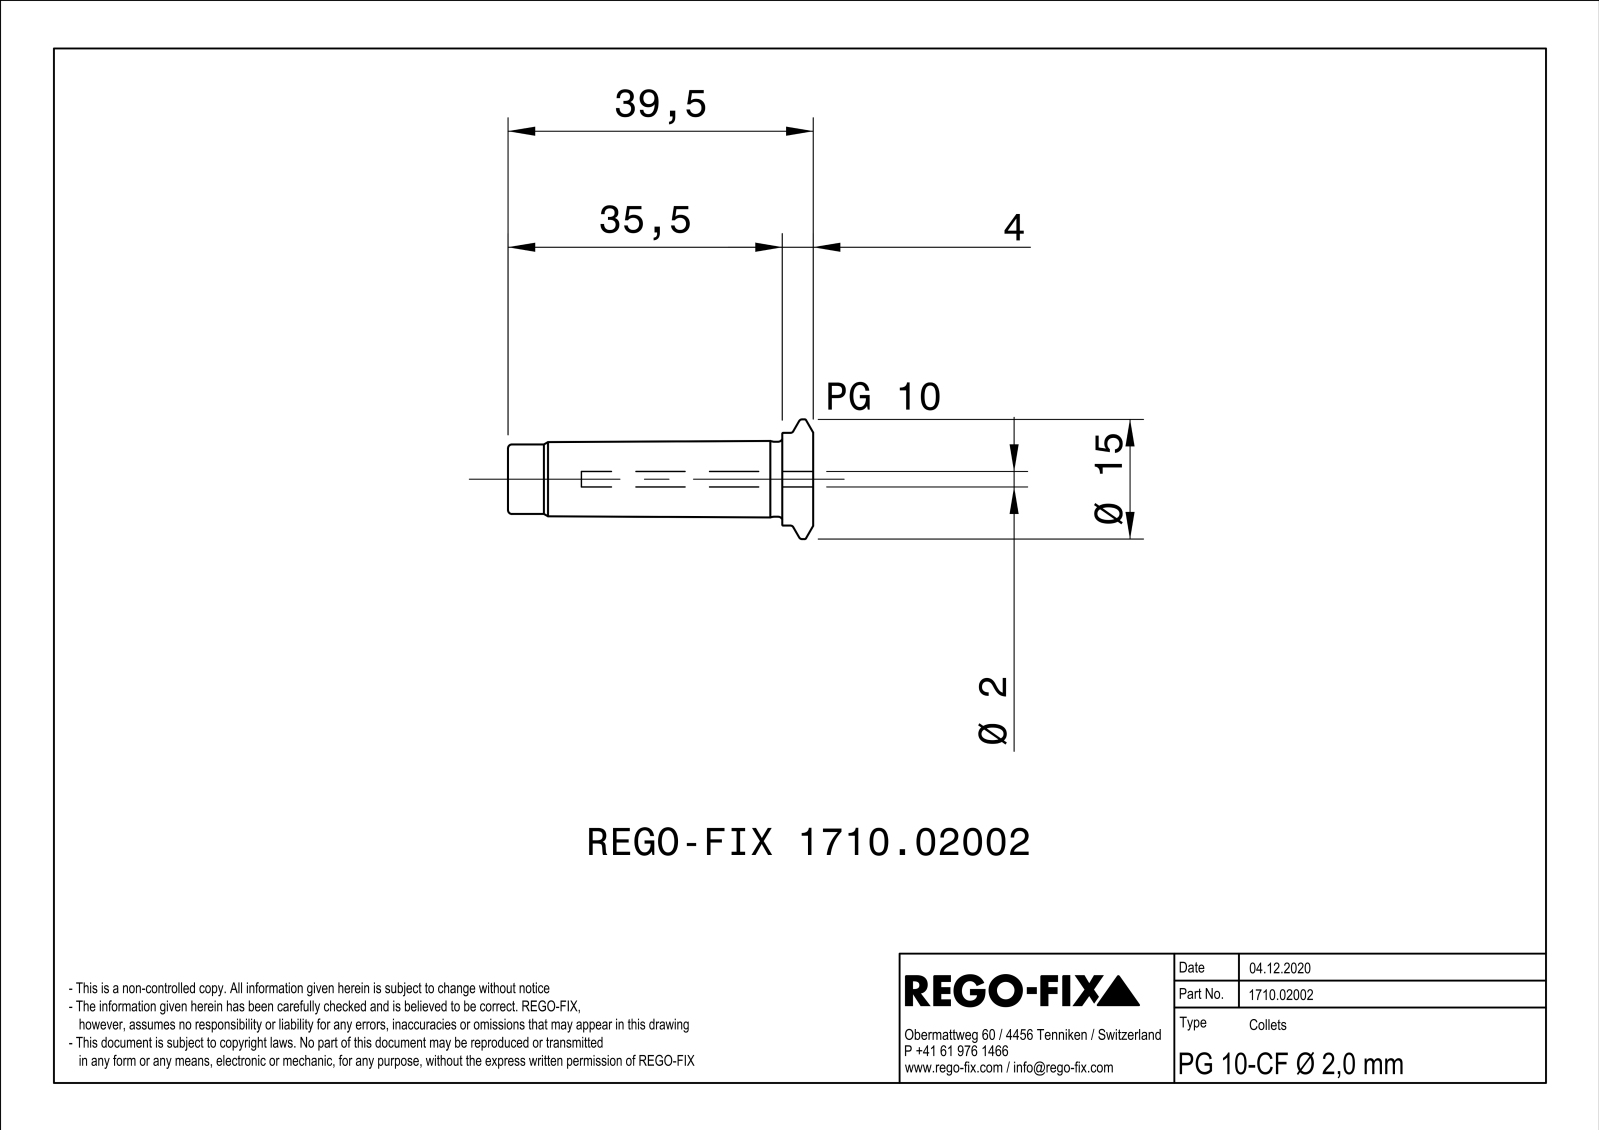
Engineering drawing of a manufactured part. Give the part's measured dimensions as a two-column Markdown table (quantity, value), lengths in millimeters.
| quantity | value |
| --- | --- |
| part name | NOCUT |
| STEP written by | SIEMENS PLM Software Solid Edge ST10 (AUTOMOTIVE_DESIGN) |
| units | millimeters |
| bodies | 0 solids, 74 faces (23 planar, 17 cylindrical, 34 other) |
| overall size | 39.5 × 15.5 × 15.49 |
| round holes (diameter × count) | 6.19 × 1 |
| round bosses / shafts (diameter × count) | 15.5 × 1, 12 × 1, 9.7 × 1, 9 × 1 |
| partial cylindrical surfaces (radius × count) | 0.4 × 3, 1 × 1 |
| main face-to-face distances | 0.8, 39.5, 4, 35.5 |
